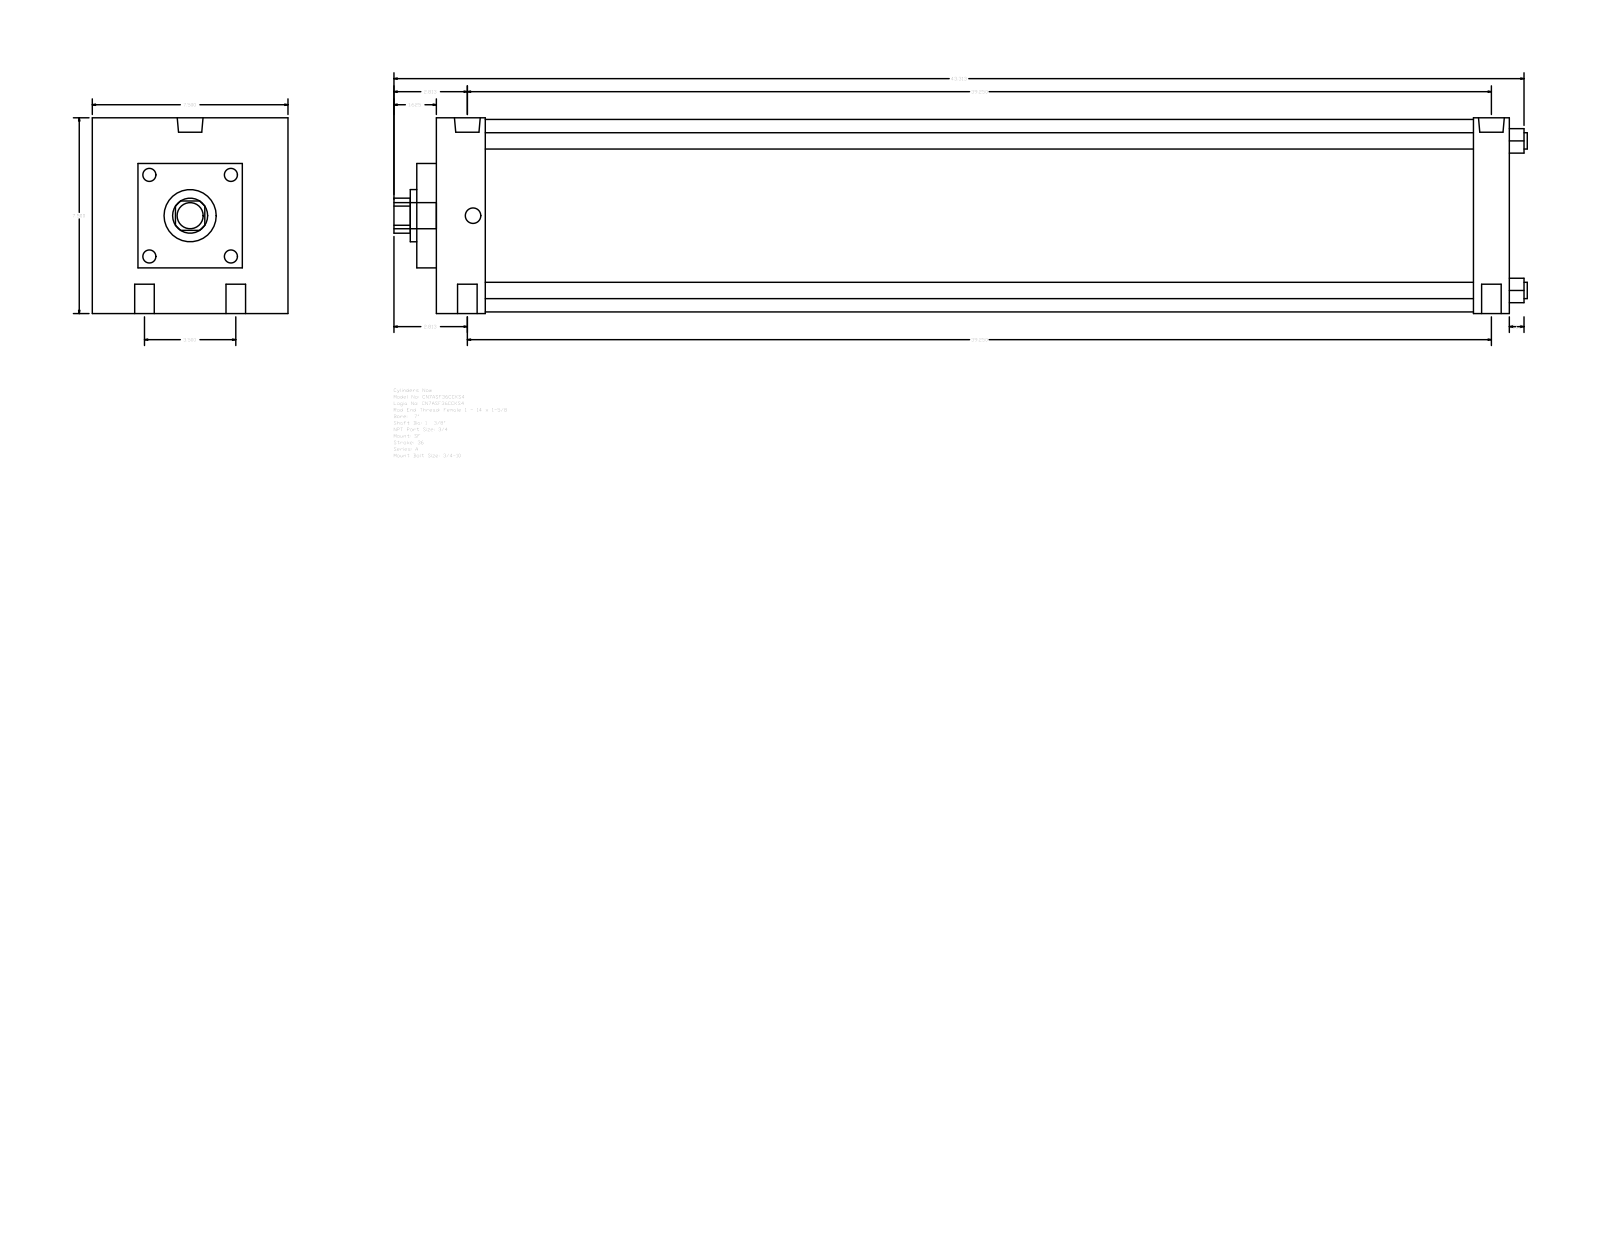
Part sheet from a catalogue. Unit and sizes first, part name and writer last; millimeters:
Units: millimetres
Overall size (bounding box): 1103.31 × 190.5 × 190.5
Round holes (diameter × count): ⌀19.05 ×4, ⌀15.08 ×2, ⌀25.12 ×2, ⌀34.92 ×1, ⌀50.8 ×1
Round bosses / shafts (diameter × count): ⌀15.88 ×4, ⌀187.32 ×1, ⌀25.4 ×1
Partial cylindrical surfaces — rounded edges, fillets, slot ends (radius × count): R17.06 ×1
Main face-to-face distances: 190.5, 1044.58, 19.04, 1063.62, 66.67, 1028.69, 47.63, 1009.65, 962.02, 996.95
Hole centre spacings: 44.45, 997.94, 996.95, 88.9, 1000.91, 985.83
Bodies: 0 solids, 93 faces (67 planar, 26 cylindrical, 0 other)
Part name (STEP PRODUCT): A_SF__0700_1.375
STEP written by: GSSL Pune (CONFIG_CONTROL_DESIGN)
